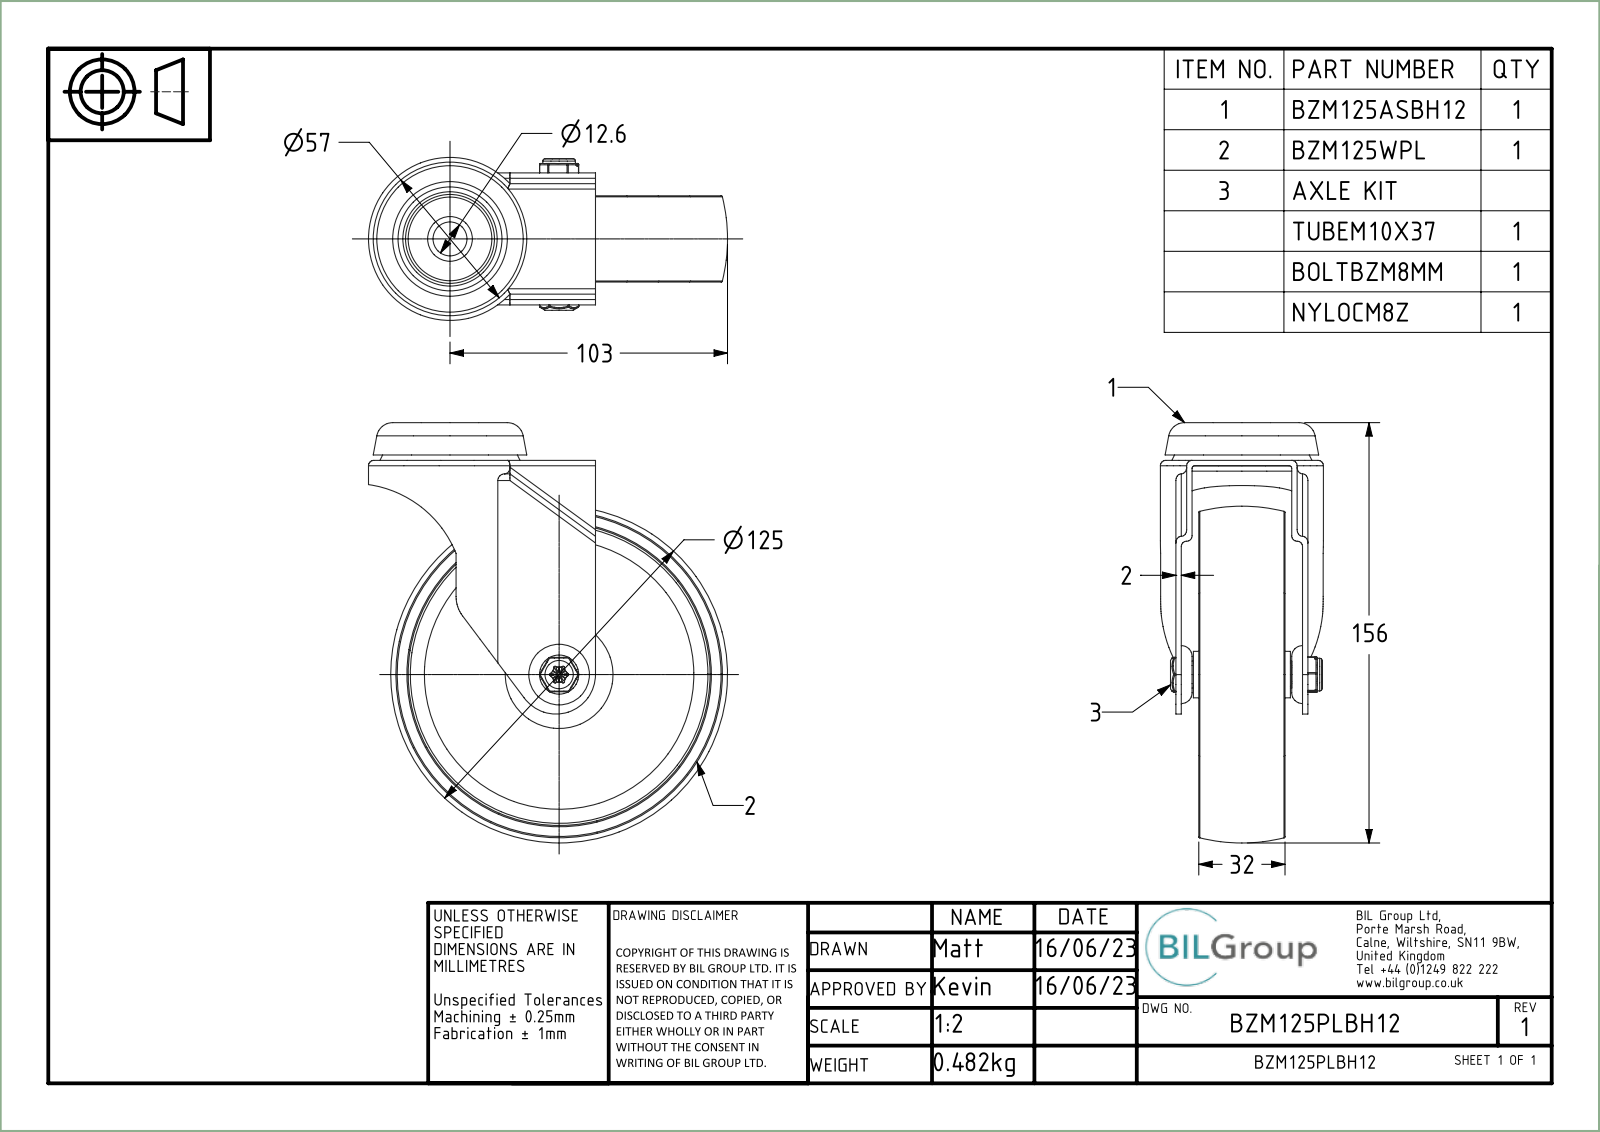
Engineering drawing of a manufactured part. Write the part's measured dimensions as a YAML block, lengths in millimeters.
part_name: "BZM125ASBH12; ZINC PLATED PRESSED STEEL HEAD; ZINC PLATED PRESSED STEEL FORKS; BZM125PLBH12 (+8 more)"
step_written_by: "Spatial InterOp 3D (CONFIG_CONTROL_DESIGN)"
units: millimeters
bodies: {solids: 7, faces: 371, planar: 65, cylindrical: 162, other: 144}
overall_size: [156, 133.25, 60.5]
volume: 158634
surface_area: 90240
round_holes:
  - {diameter: 8, count: 1}
  - {diameter: 8.2, count: 1}
  - {diameter: 8.5, count: 1}
  - {diameter: 8.6, count: 1}
  - {diameter: 10.2, count: 1}
  - {diameter: 10.3, count: 1}
  - {diameter: 12.6, count: 1}
  - {diameter: 46, count: 1}
round_bosses_or_shafts:
  - {diameter: 48, count: 1}
  - {diameter: 30, count: 1}
  - {diameter: 17.25, count: 1}
  - {diameter: 12.1, count: 1}
  - {diameter: 10, count: 1}
  - {diameter: 6, count: 1}
partial_cylinders:
  - {radius: 0.5, count: 30}
  - {radius: 2, count: 22}
  - {radius: 1, count: 2}
  - {radius: 2.75, count: 1}
  - {radius: 12, count: 1}
  - {radius: 14.65, count: 1}
  - {radius: 28.25, count: 1}
  - {radius: 30.25, count: 1}
face_to_face_distances: [2, 3.5, 22.75, 26.25, 4, 47, 20.75, 24.25, 6.5, 40.5]
